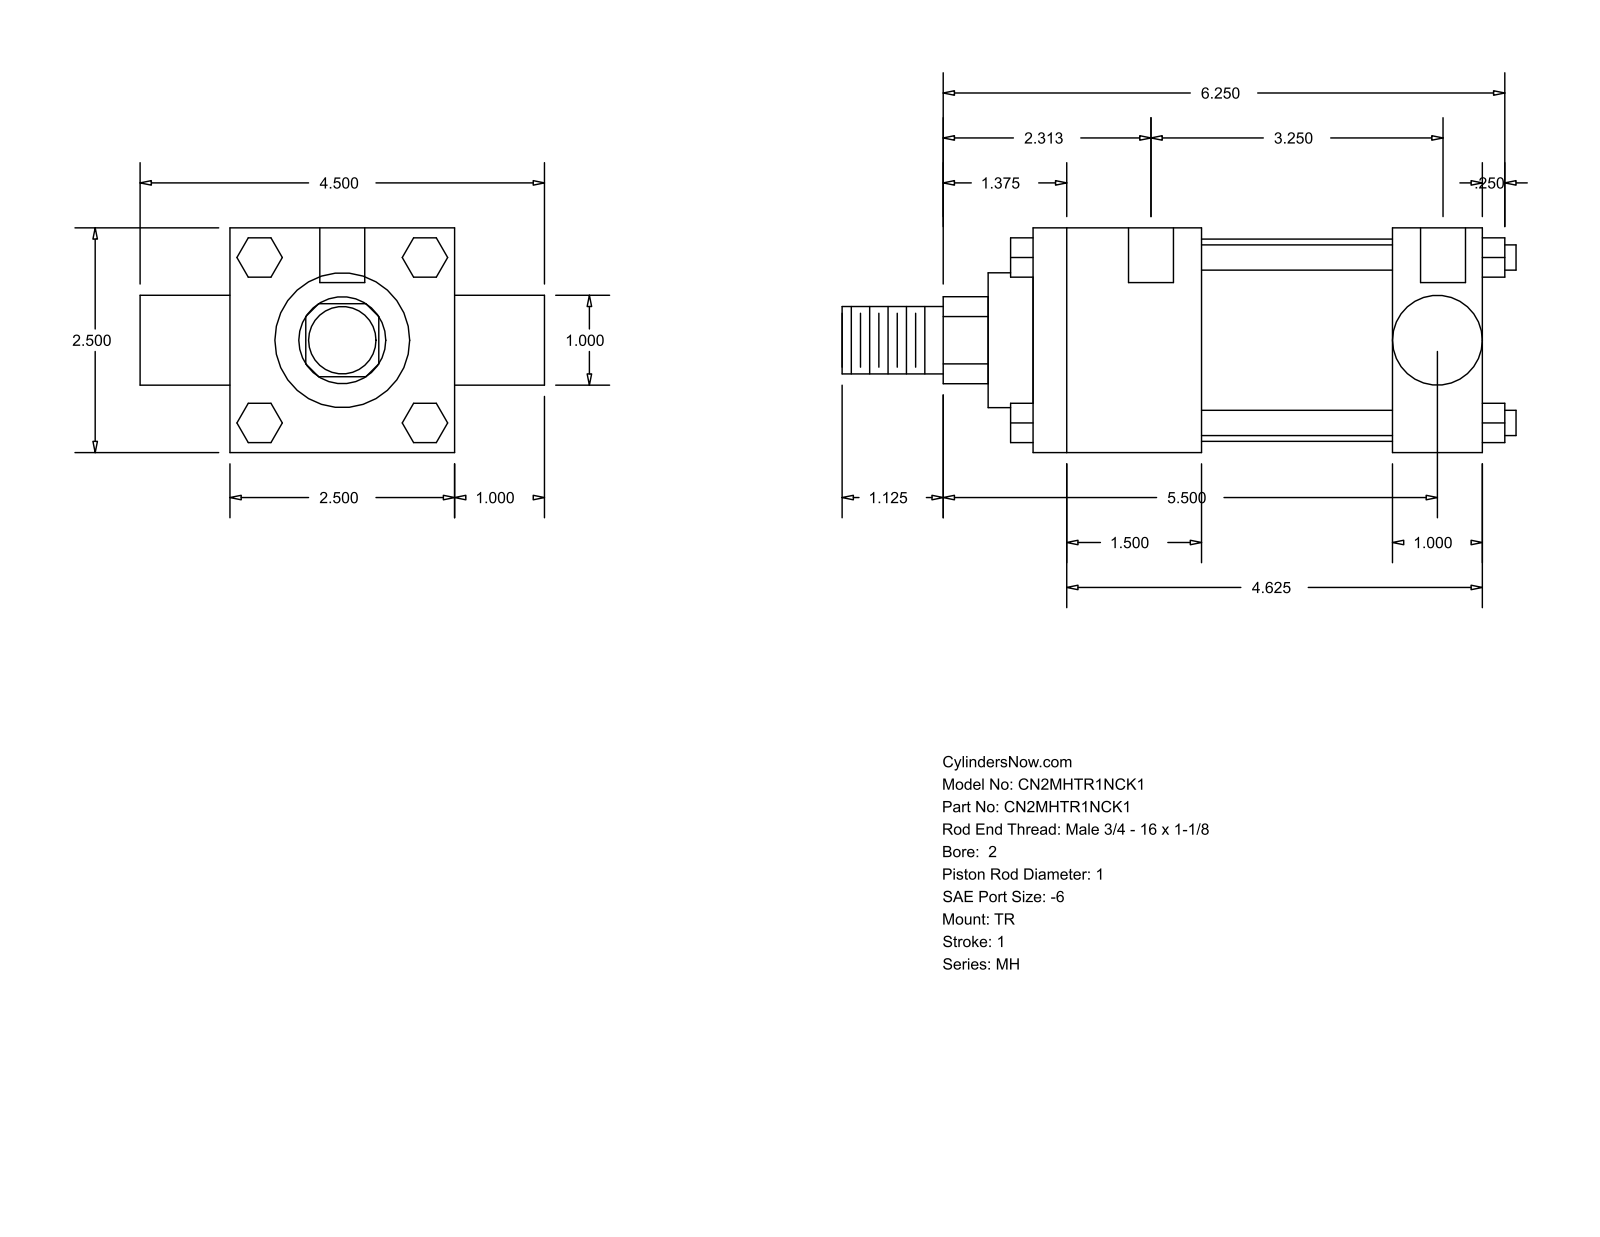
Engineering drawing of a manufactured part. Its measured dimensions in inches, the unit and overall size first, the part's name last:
Units: inches
Overall size (bounding box): 7.5 × 4.5 × 2.5
Round holes (diameter × count): ⌀0.219 ×3, ⌀0.5 ×2
Round bosses / shafts (diameter × count): ⌀0.281 ×4, ⌀2.25 ×1, ⌀1.5 ×1, ⌀1 ×1, ⌀0.998 ×1, ⌀0.75 ×1
Partial cylindrical surfaces — rounded edges, fillets, slot ends (radius × count): R0.484 ×1
Main face-to-face distances: 2.5, 5, 1, 2.125, 4, 1.875, 3.125, 3.5, 4.5, 5.5
Hole centre spacings: 0.125, 0.187, 3.25, 3.375, 3.437, 3.562
Bodies: 0 solids, 120 faces (92 planar, 28 cylindrical, 0 other)
Part name (STEP PRODUCT): MH_TR__0200_1
STEP written by: GSSL Pune (CONFIG_CONTROL_DESIGN)
